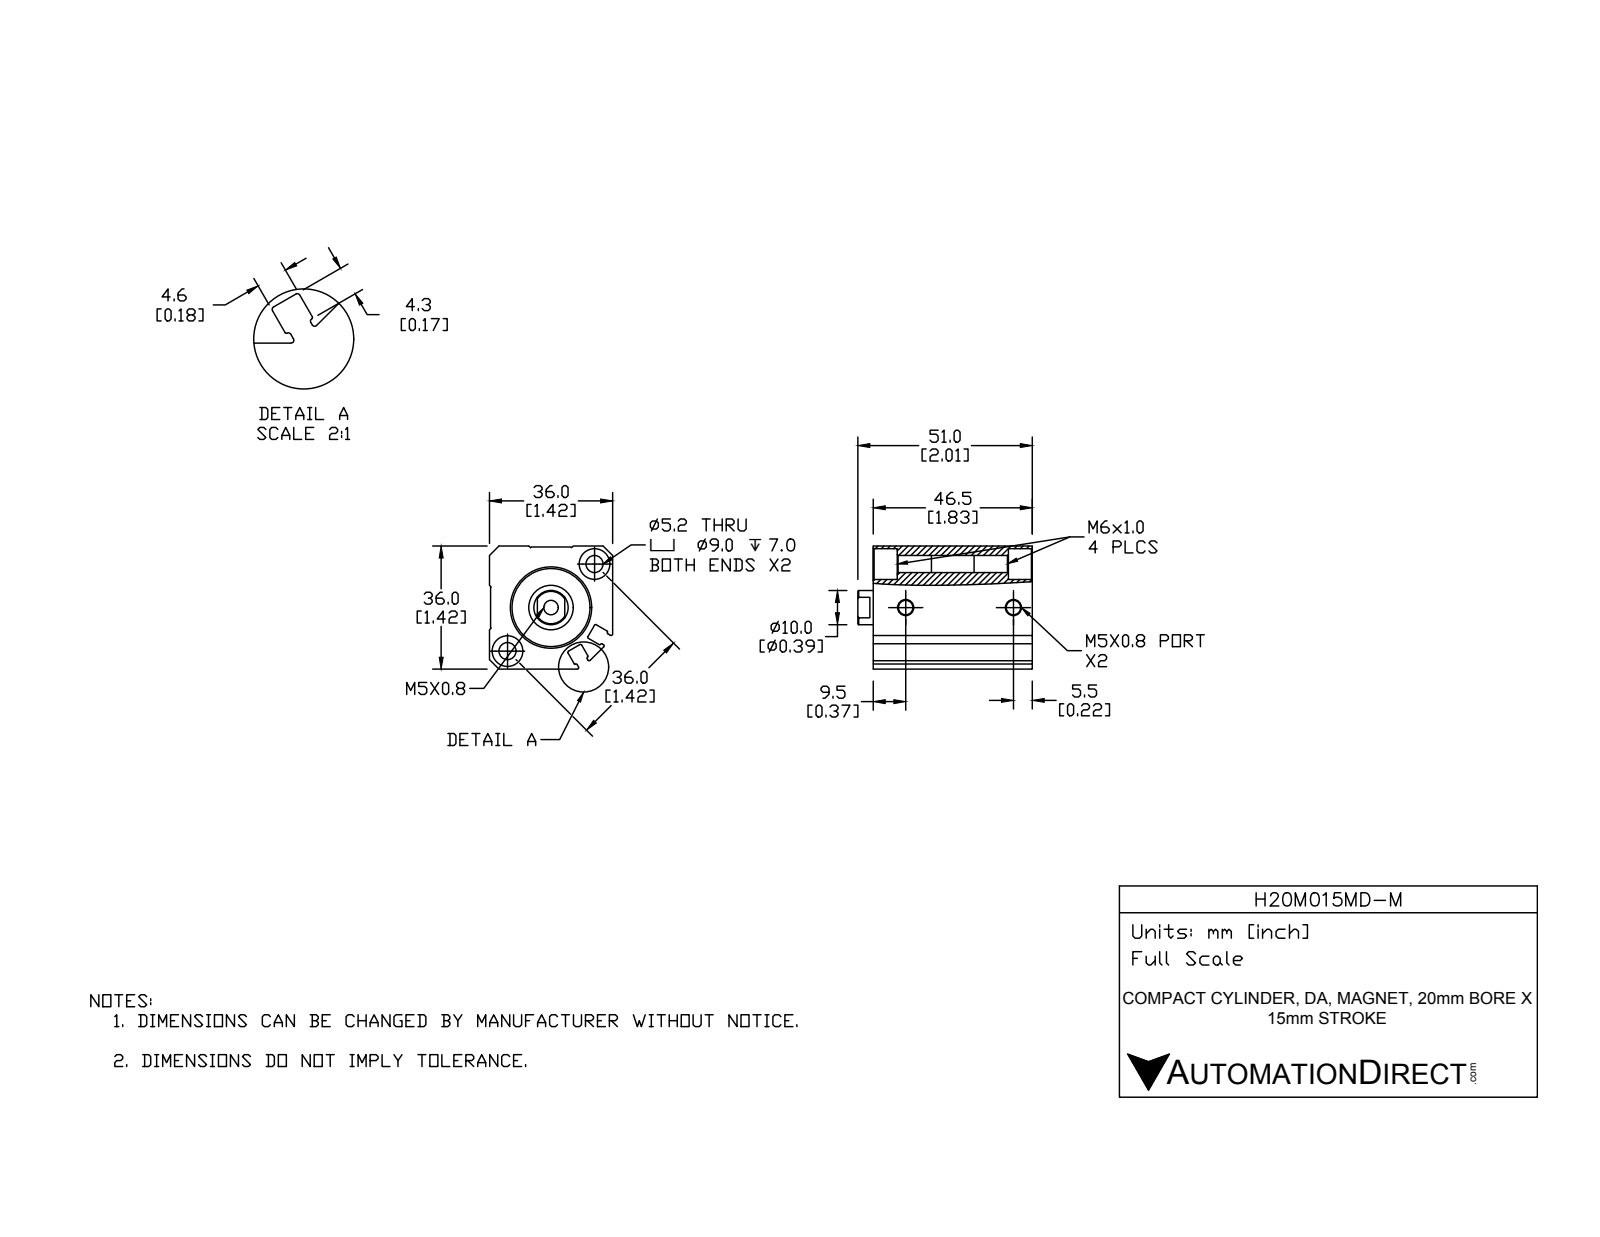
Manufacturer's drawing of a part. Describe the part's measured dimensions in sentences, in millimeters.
The part is named "H20M015MD-M; H20M015MD-M-BODY; H20M015MD-M-PISTON". Its 3-D file was written by "SolidWorks 2015 (CONFIG_CONTROL_DESIGN)". It is 2 solids with 141 faces: 53 planar, 55 cylindrical and 33 other. Overall it measures 51 by 36 by 36 millimeters. Its volume is 47 212 cubic millimeters and its surface area 17 599 square millimeters. Round holes: 3 of diameter 4.2, 2 of diameter 5, 2 of diameter 9, 1 of diameter 10, 1 of diameter 13, 1 of diameter 20, 1 of diameter 22.8. Round bosses or shafts: 1 of diameter 11. Partial cylindrical surfaces (rounded edges, fillets, slot ends): 12 of radius 0.4, 4 of radius 0.2. The main face-to-face distances are 36, 35.7, 4, 46.5, 42.5, 2.6, 4.6, 1.4, 45.1, 35.5. The hole center spacings are 18, 31.5, 36.01.
